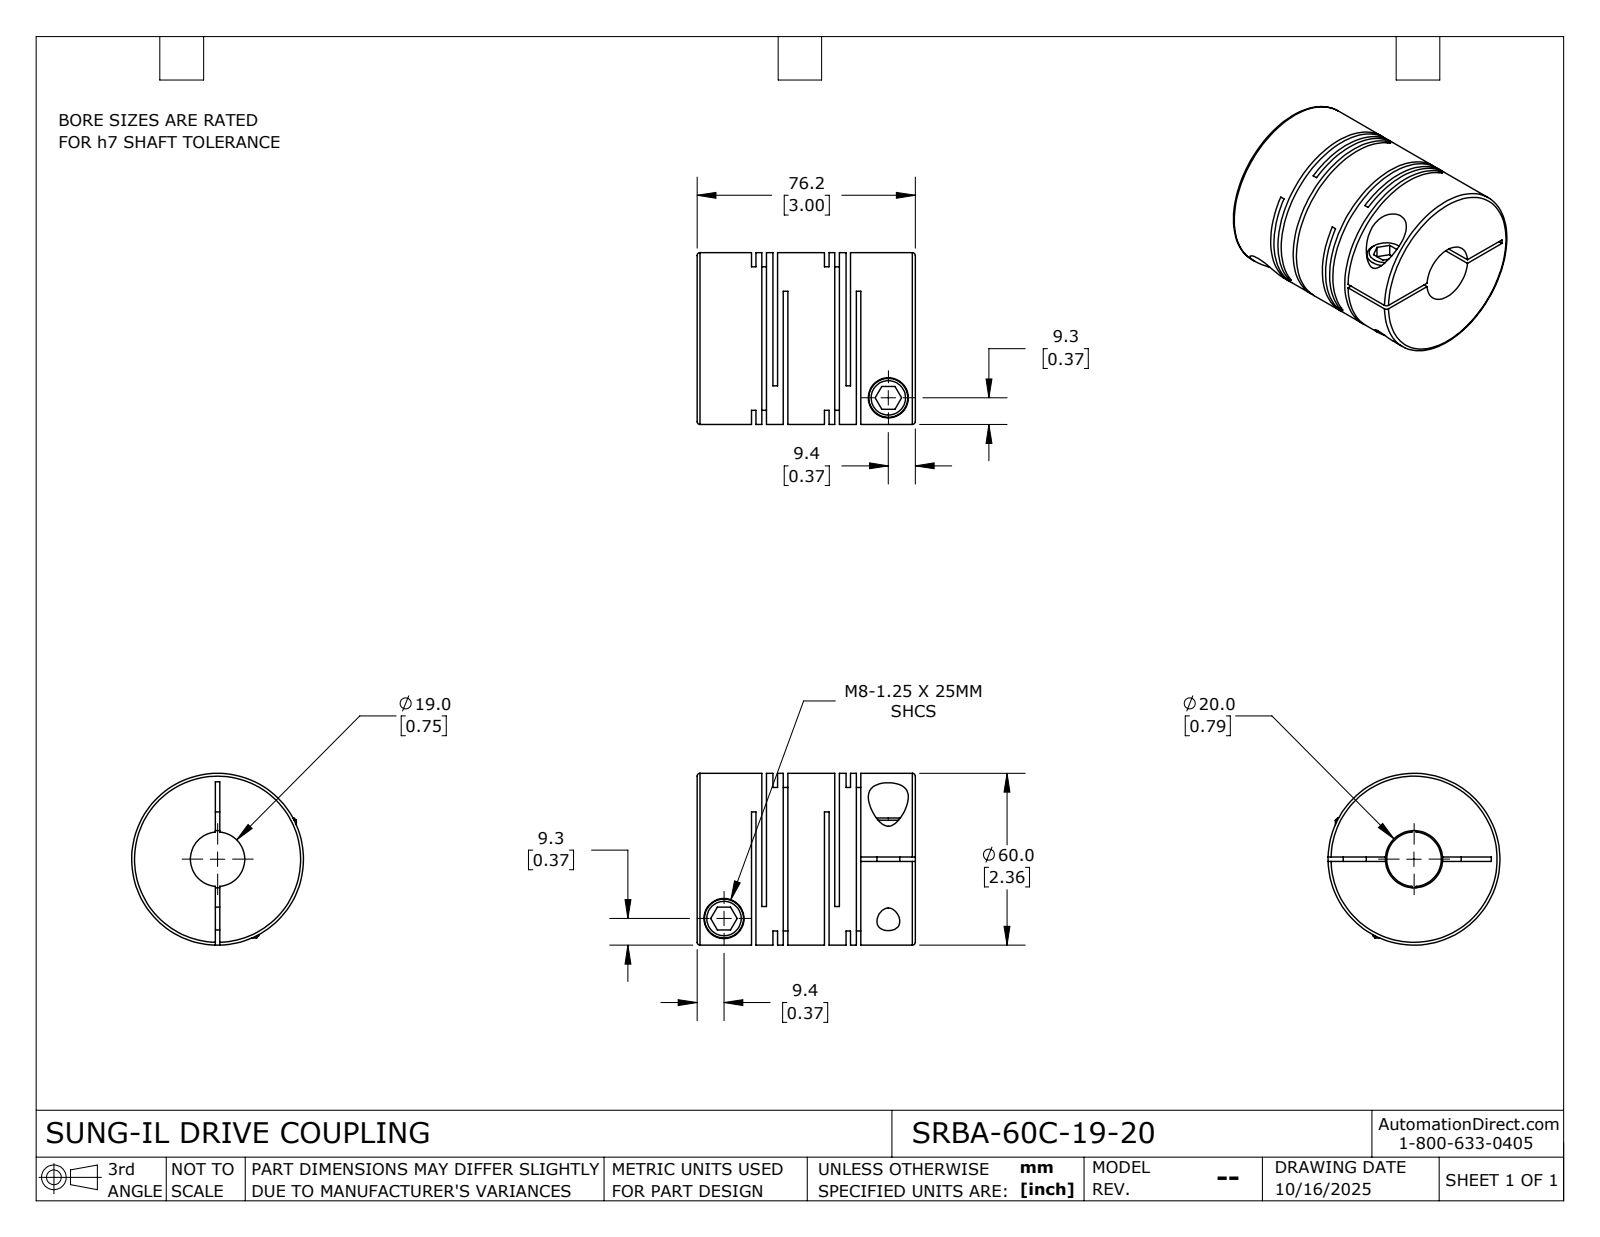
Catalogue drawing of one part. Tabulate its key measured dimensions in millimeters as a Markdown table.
| quantity | value |
| --- | --- |
| part name | SRBA-60C-19-20 |
| STEP written by | SolidWorks 2024 (CONFIG_CONTROL_DESIGN) |
| units | millimeters |
| bodies | 1 solid, 115 faces (60 planar, 42 cylindrical, 13 other) |
| overall size | 76.2 × 60 × 60 |
| volume | 160 831 mm³ |
| surface area | 59 158 mm² |
| round holes (diameter × count) | 8 × 2, 14 × 2, 19 × 1, 20 × 1 |
| round bosses / shafts (diameter × count) | 13.6 × 2, 60 × 1 |
| main face-to-face distances | 1.6, 3.6, 7.5, 25.5, 33, 2, 5.9, 23.9, 3.9, 18 |
